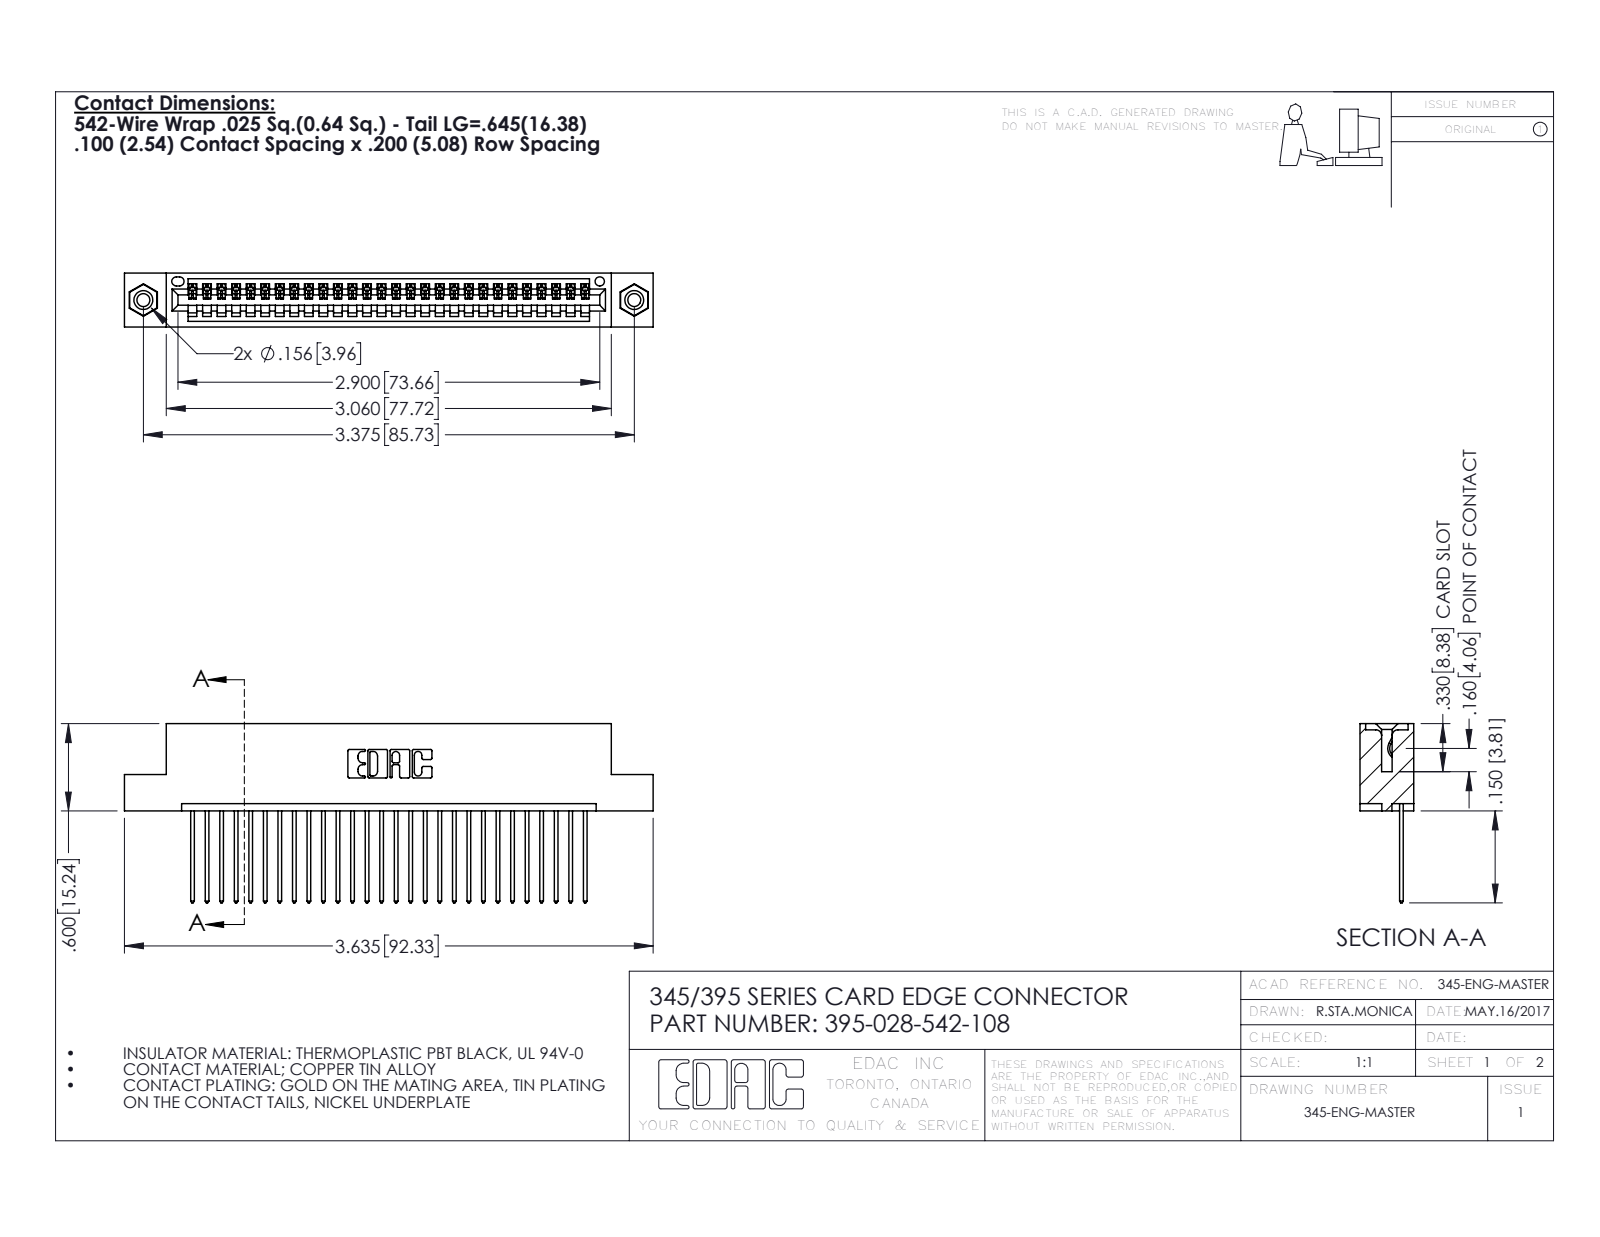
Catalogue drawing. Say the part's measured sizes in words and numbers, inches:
The part is named "345 Part_Flush Mounting Lugs - 0.156 Dia-TI; 395-028-542-108; 345-250-001_345-250-003-102; 345-292-001_345-293-142". Its 3-D file was written by "SolidWorks 2016 (CONFIG_CONTROL_DESIGN)". It is 31 solids with 1810 faces: 1232 planar, 562 cylindrical and 16 other. Overall it measures 3.635 by 1.232 by 0.37 inches. Its volume is 0.532 cubic inches and its surface area 18.29 square inches. Round holes: 2 of diameter 0.089, 2 of diameter 0.125, 2 of diameter 0.156, 1 of diameter 0.064. Round bosses or shafts: 2 of diameter 0.155. Partial cylindrical surfaces (rounded edges, fillets, slot ends): 56 of radius 0.006, 56 of radius 0.01, 22 of radius 0.01, 6 of radius 0.007, 6 of radius 0.031, 3 of radius 0.026, 2 of radius 0.031, 2 of radius 0.04. The main face-to-face distances are 0.072, 0.298, 0.2, 0.37, 0.098, 0.272, 0.025, 0.225, 0.149, 0.072. The hole center spacings are 0.27, 3.14, 3.375.
